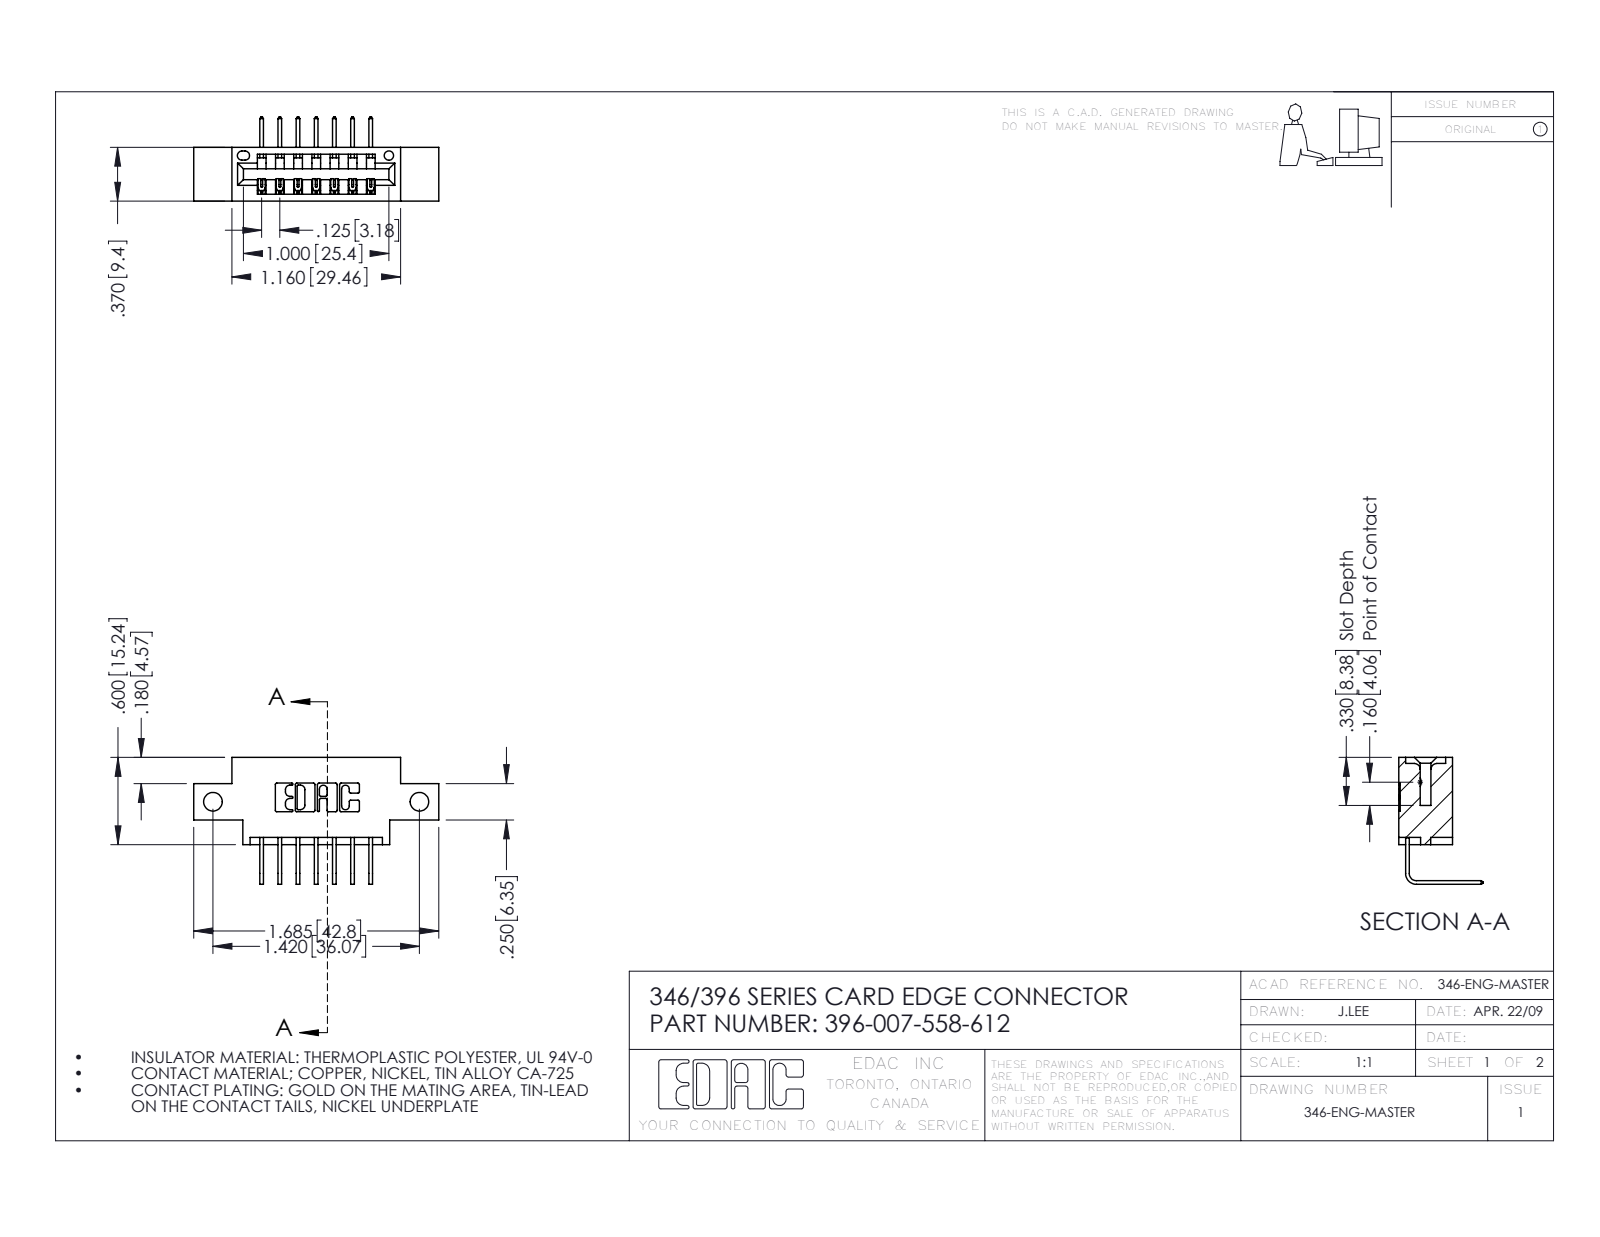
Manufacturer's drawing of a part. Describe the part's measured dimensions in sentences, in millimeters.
The part is named "345-292-001_558 Tail - 2; 346 Part_0.170 Offset - Side Mount; 396-007-558-612". Its 3-D file was written by "SolidWorks 2016 (CONFIG_CONTROL_DESIGN)". It is 8 solids with 546 faces: 374 planar, 172 cylindrical and 0 other. Overall it measures 42.8 by 22.2 by 14.7 millimeters. Its volume is 3 640 cubic millimeters and its surface area 4 322 square millimeters. Round holes: 2 of diameter 3.3, 1 of diameter 1.6. Partial cylindrical surfaces (rounded edges, fillets, slot ends): 22 of radius 0.3, 14 of radius 0.2, 6 of radius 0.2, 6 of radius 0.8, 3 of radius 0.7, 2 of radius 0.8, 2 of radius 1, 1 of radius 0.4. The main face-to-face distances are 6.4, 9.4, 8.2, 1.2, 7.6, 0.6, 3.8, 5.6, 2.5, 4.4. The hole center spacings are 36.1.
